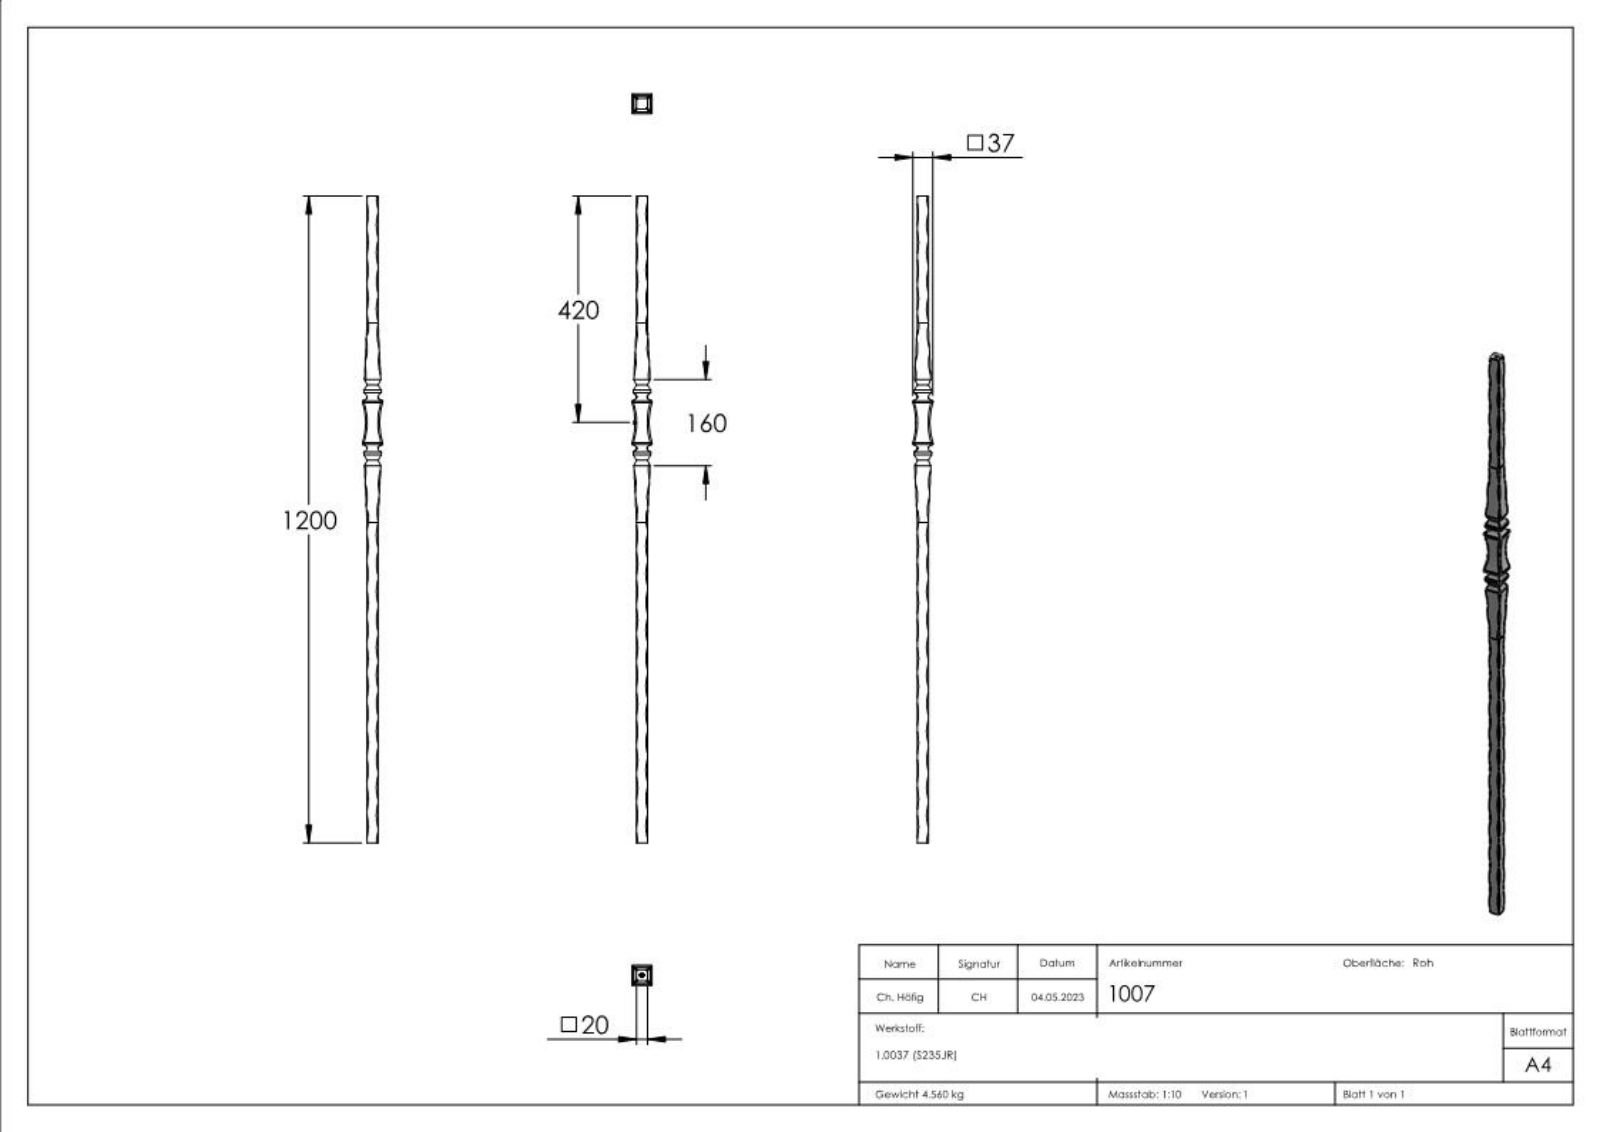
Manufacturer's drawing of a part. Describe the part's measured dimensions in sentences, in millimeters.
The part is named "1007". Its 3-D file was written by "SolidWorks 2018 (CONFIG_CONTROL_DESIGN)". It is 1 solid with 352 faces: 156 planar, 4 cylindrical and 192 other. Overall it measures 1200 by 37 by 37 millimeters. Its volume is 586 322 cubic millimeters and its surface area 106 356 square millimeters. Partial cylindrical surfaces (rounded edges, fillets, slot ends): 4 of radius 127.2. The main face-to-face distances are 20, 37.58, 6, 26, 89.12, 44.7, 2.5, 8.5, 28.5, 34.5.
